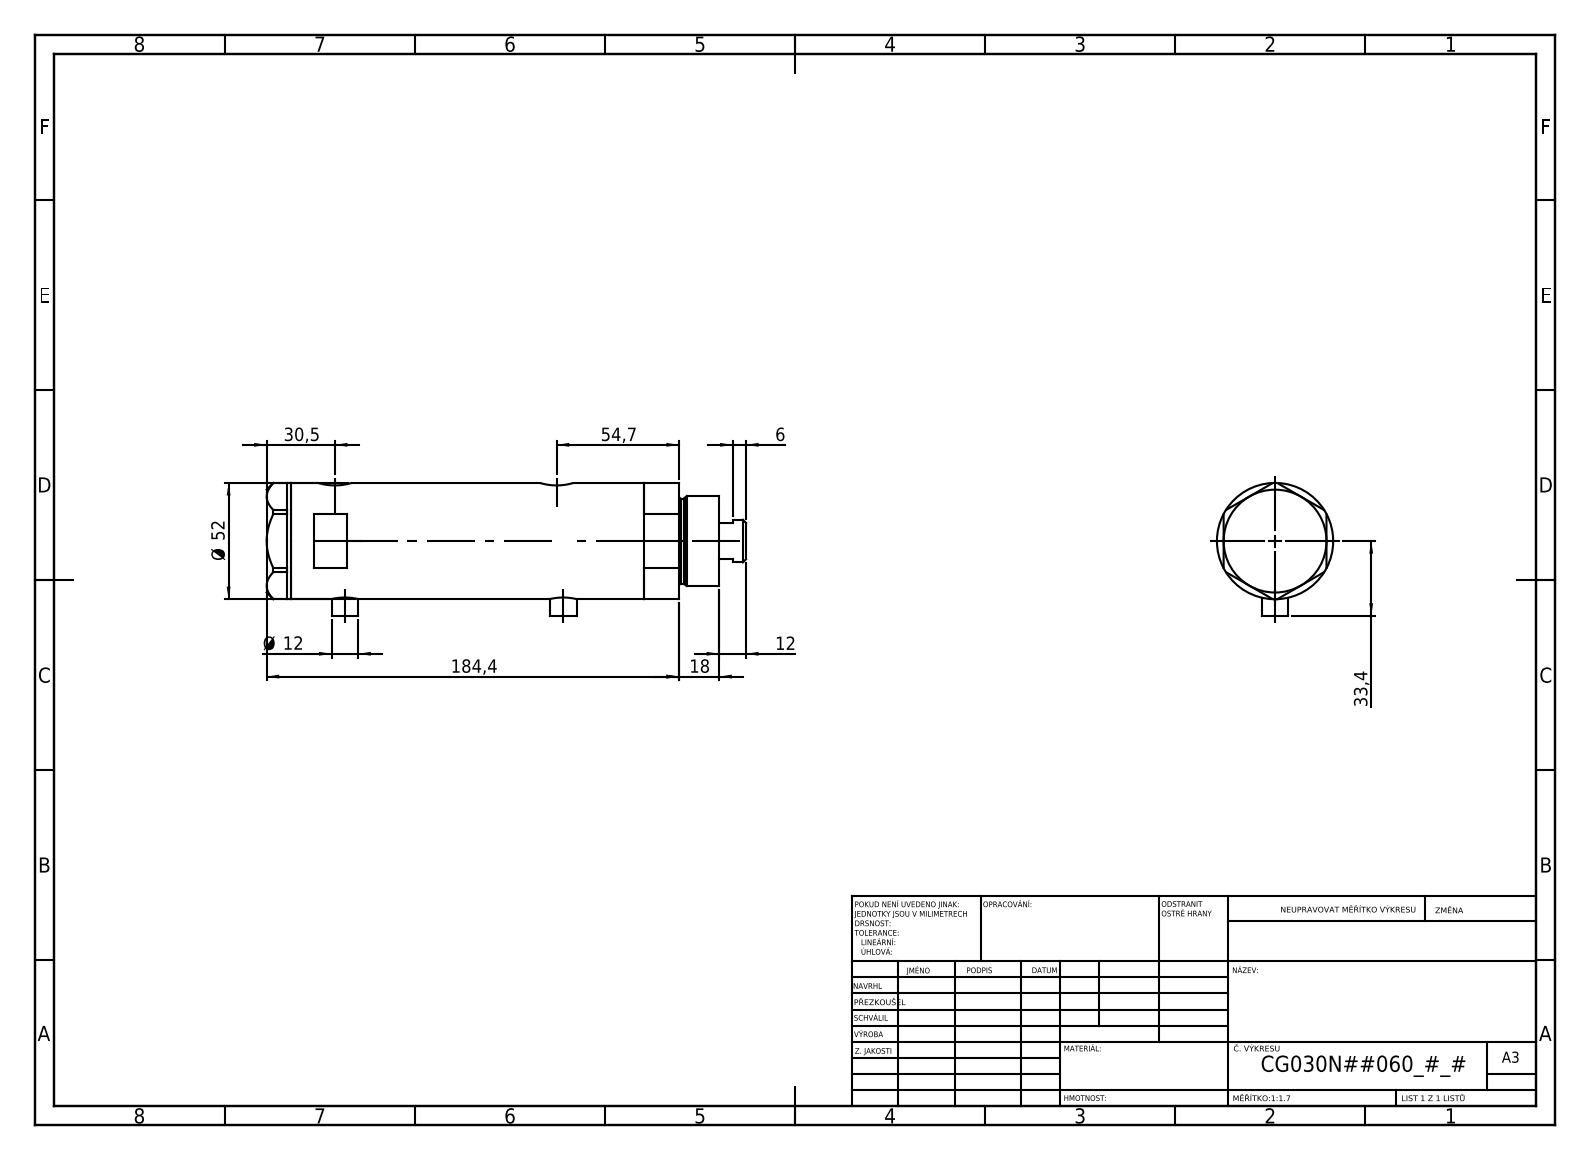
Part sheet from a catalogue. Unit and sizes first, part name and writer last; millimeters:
Units: millimetres
Overall size (bounding box): 214.4 × 59.4 × 52
Round holes (diameter × count): ⌀9.73 ×2, ⌀12.5 ×2, ⌀15 ×2, ⌀6.5 ×1, ⌀20 ×1, ⌀21.5 ×1, ⌀30 ×1, ⌀33 ×1, ⌀44 ×1
Round bosses / shafts (diameter × count): ⌀12 ×2, ⌀52 ×1, ⌀40 ×1, ⌀38 ×1, ⌀19 ×1
Main face-to-face distances: 121.5, 23.8, 97.7, 11, 34.8, 132.5, 46, 168.9, 157.9, 134.1
Hole centre spacings: 2.9, 4.5, 94.7, 97.6, 99.2, 102.1
Volume: 386 850 mm³ · Surface area: 86 748 mm²
Bodies: 4 solids, 134 faces (65 planar, 49 cylindrical, 20 other)
Part name (STEP PRODUCT): V270CG_FRONT; V270CG_MIDDLE; V270CG_VC; V270CG_BACK
STEP written by: SolidWorks 2019 (CONFIG_CONTROL_DESIGN)
